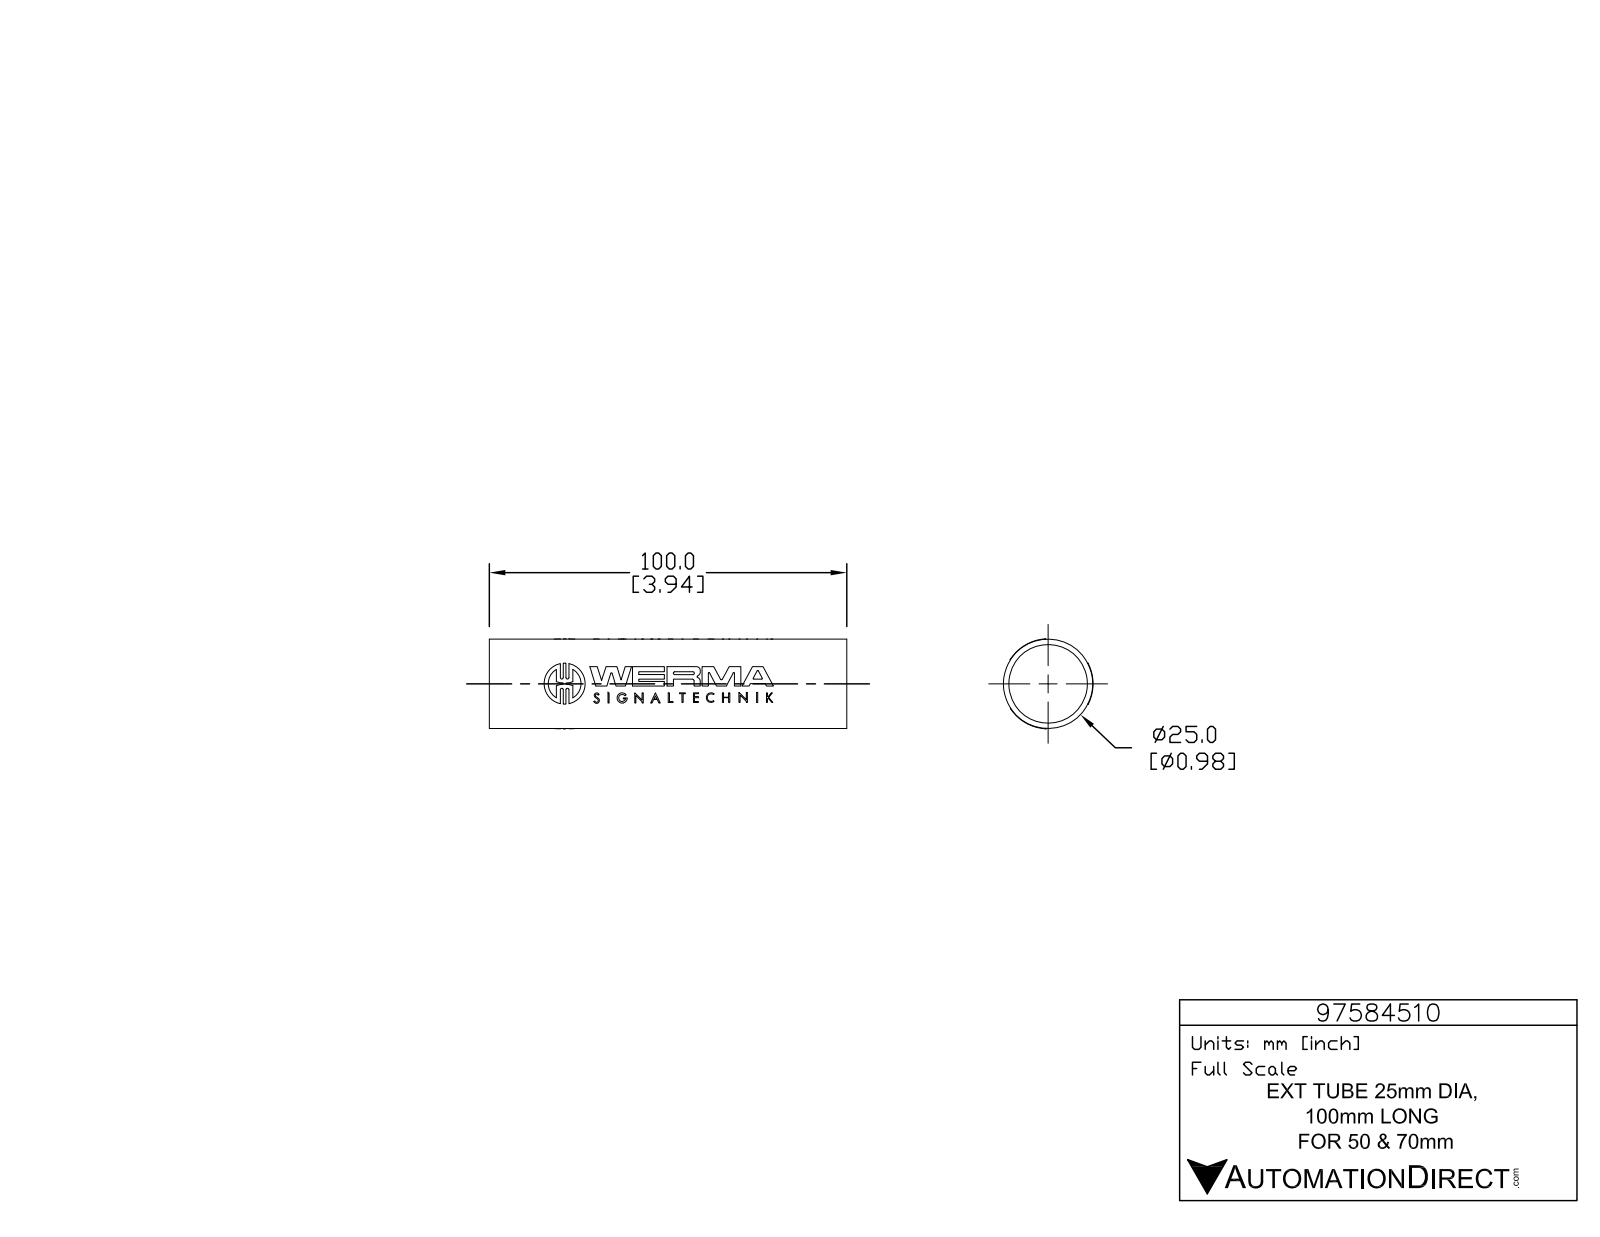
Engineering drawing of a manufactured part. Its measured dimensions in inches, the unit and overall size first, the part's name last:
Units: inches
Overall size (bounding box): 3.937 × 0.991 × 0.988
Round holes (diameter × count): ⌀0.078 ×3, ⌀0.866 ×1
Round bosses / shafts (diameter × count): ⌀0.452 ×3, ⌀0.113 ×3, ⌀0.984 ×1
Partial cylindrical surfaces — rounded edges, fillets, slot ends (radius × count): R0.007 ×9, R0.007 ×6, R0.016 ×6, R0.016 ×6, R0.016 ×6, R0.262 ×6, R0.006 ×3, R0.006 ×3
Main face-to-face distances: 3.937, 0.213, 0.075, 0.033, 0.061, 0.138, 0.05, 0.031, 0.182, 0.232
Volume: 0.681 in³ · Surface area: 23.47 in²
Bodies: 1 solid, 752 faces (521 planar, 231 cylindrical, 0 other)
Part name (STEP PRODUCT): 97584510
STEP written by: SolidWorks 2015 (AUTOMOTIVE_DESIGN)
